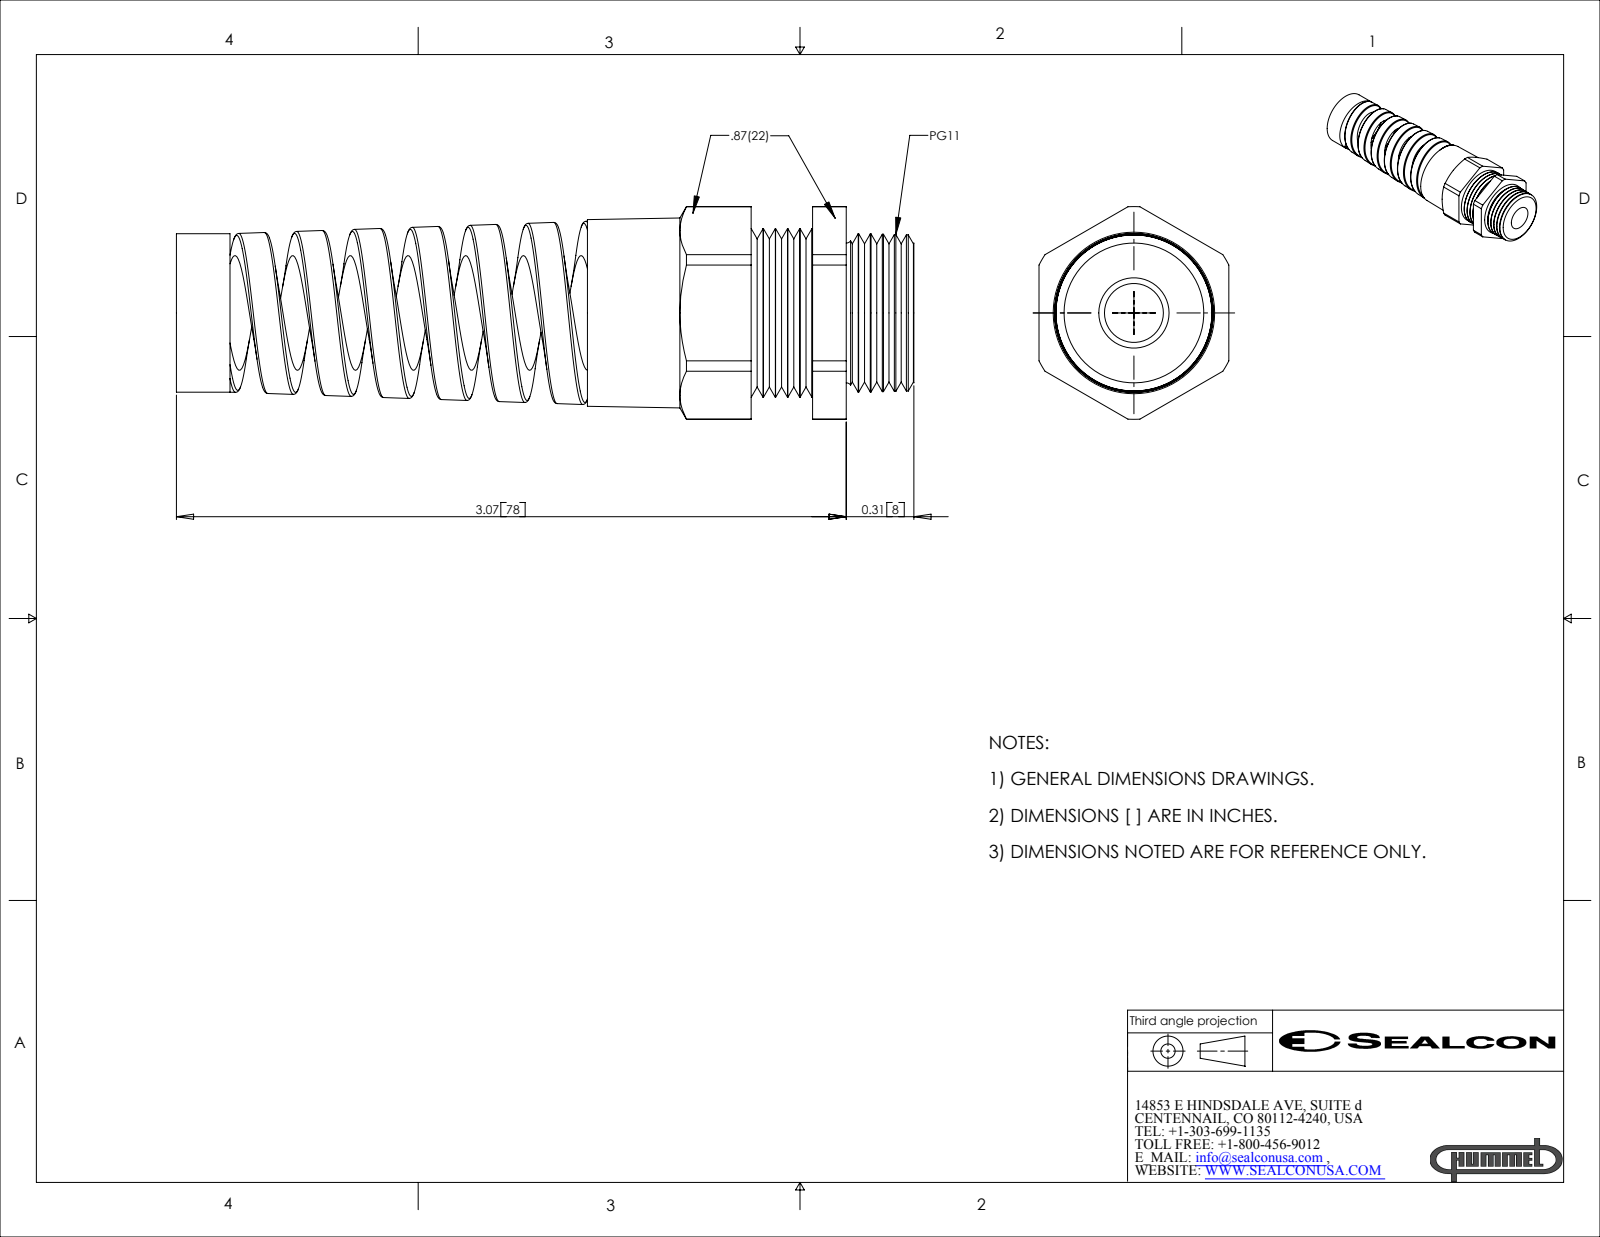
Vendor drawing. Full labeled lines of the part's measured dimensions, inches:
Part name (STEP PRODUCT): CF11AR-GY
STEP written by: SolidWorks 2007 (CONFIG_CONTROL_DESIGN)
Units: inches
Bodies: 1 solid, 153 faces (19 planar, 42 cylindrical, 92 other)
Overall size (bounding box): 3.38 × 0.974 × 0.87
Volume: 0.974 in³ · Surface area: 16.28 in²
Round holes (diameter × count): ⌀0.27 ×1, ⌀0.526 ×1
Round bosses / shafts (diameter × count): ⌀0.774 ×1, ⌀0.726 ×1
Partial cylindrical surfaces — rounded edges, fillets, slot ends (radius × count): R0.487 ×1
Main face-to-face distances: 0.87, 1.496, 1.186, 0.31, 1.884, 3.07, 3.38, 2.916, 1.032, 0.154
